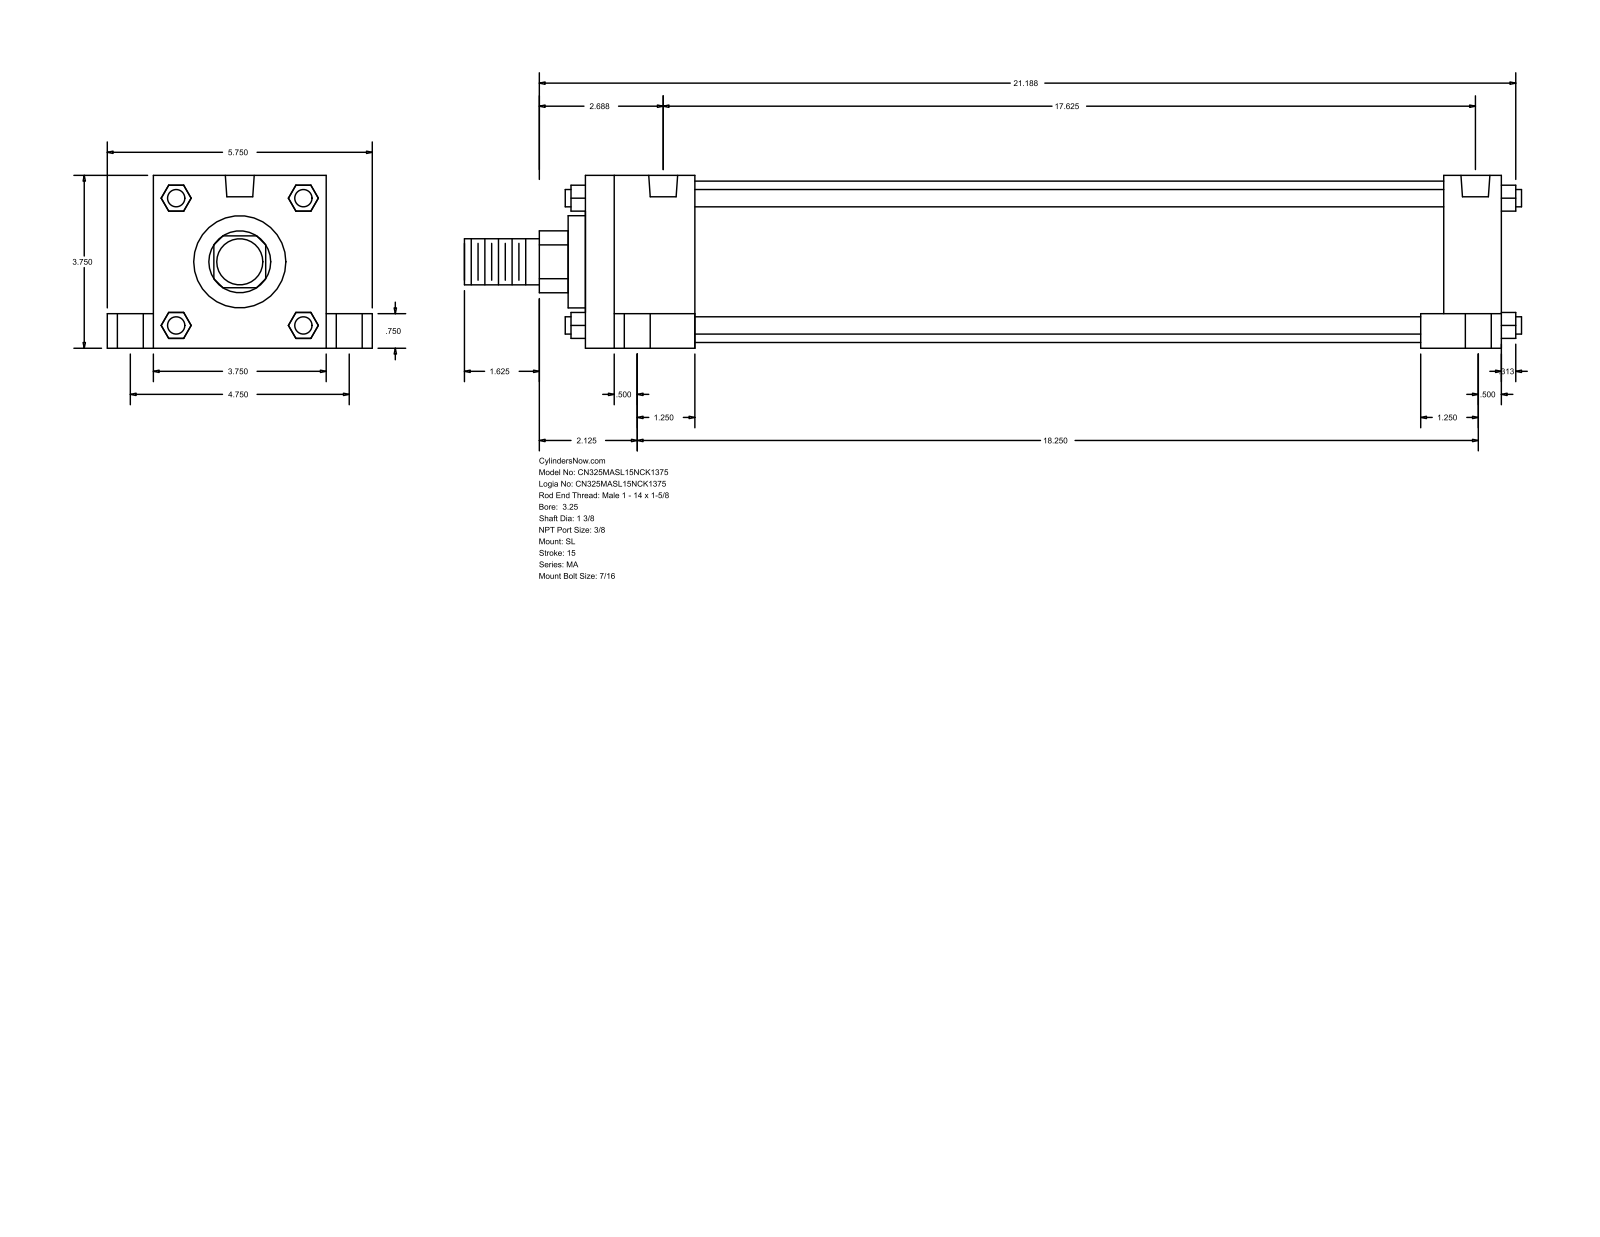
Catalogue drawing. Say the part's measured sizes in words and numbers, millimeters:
The part is named "MA_SL__0325_1.375". Its 3-D file was written by "GSSL Pune (CONFIG_CONTROL_DESIGN)". It is 0 solids with 148 faces: 112 planar, 36 cylindrical and 0 other. Overall it measures 582.61 by 146.05 by 95.25 millimeters. Round holes: 4 of diameter 11.11, 4 of diameter 14.29, 4 of diameter 20.64, 2 of diameter 15.93. Round bosses or shafts: 4 of diameter 9.53, 1 of diameter 88.9, 1 of diameter 50.8, 1 of diameter 34.92, 1 of diameter 25.4. Partial cylindrical surfaces (rounded edges, fillets, slot ends): 1 of radius 17.06. The main face-to-face distances are 95.24, 504.83, 25.41, 120.65, 473.08, 31.75, 60.32, 412.76, 444.51, 19.05. The hole center spacings are 60.35, 60.66, 62, 63.27, 120.66, 438.15, 448.57, 453.29.
